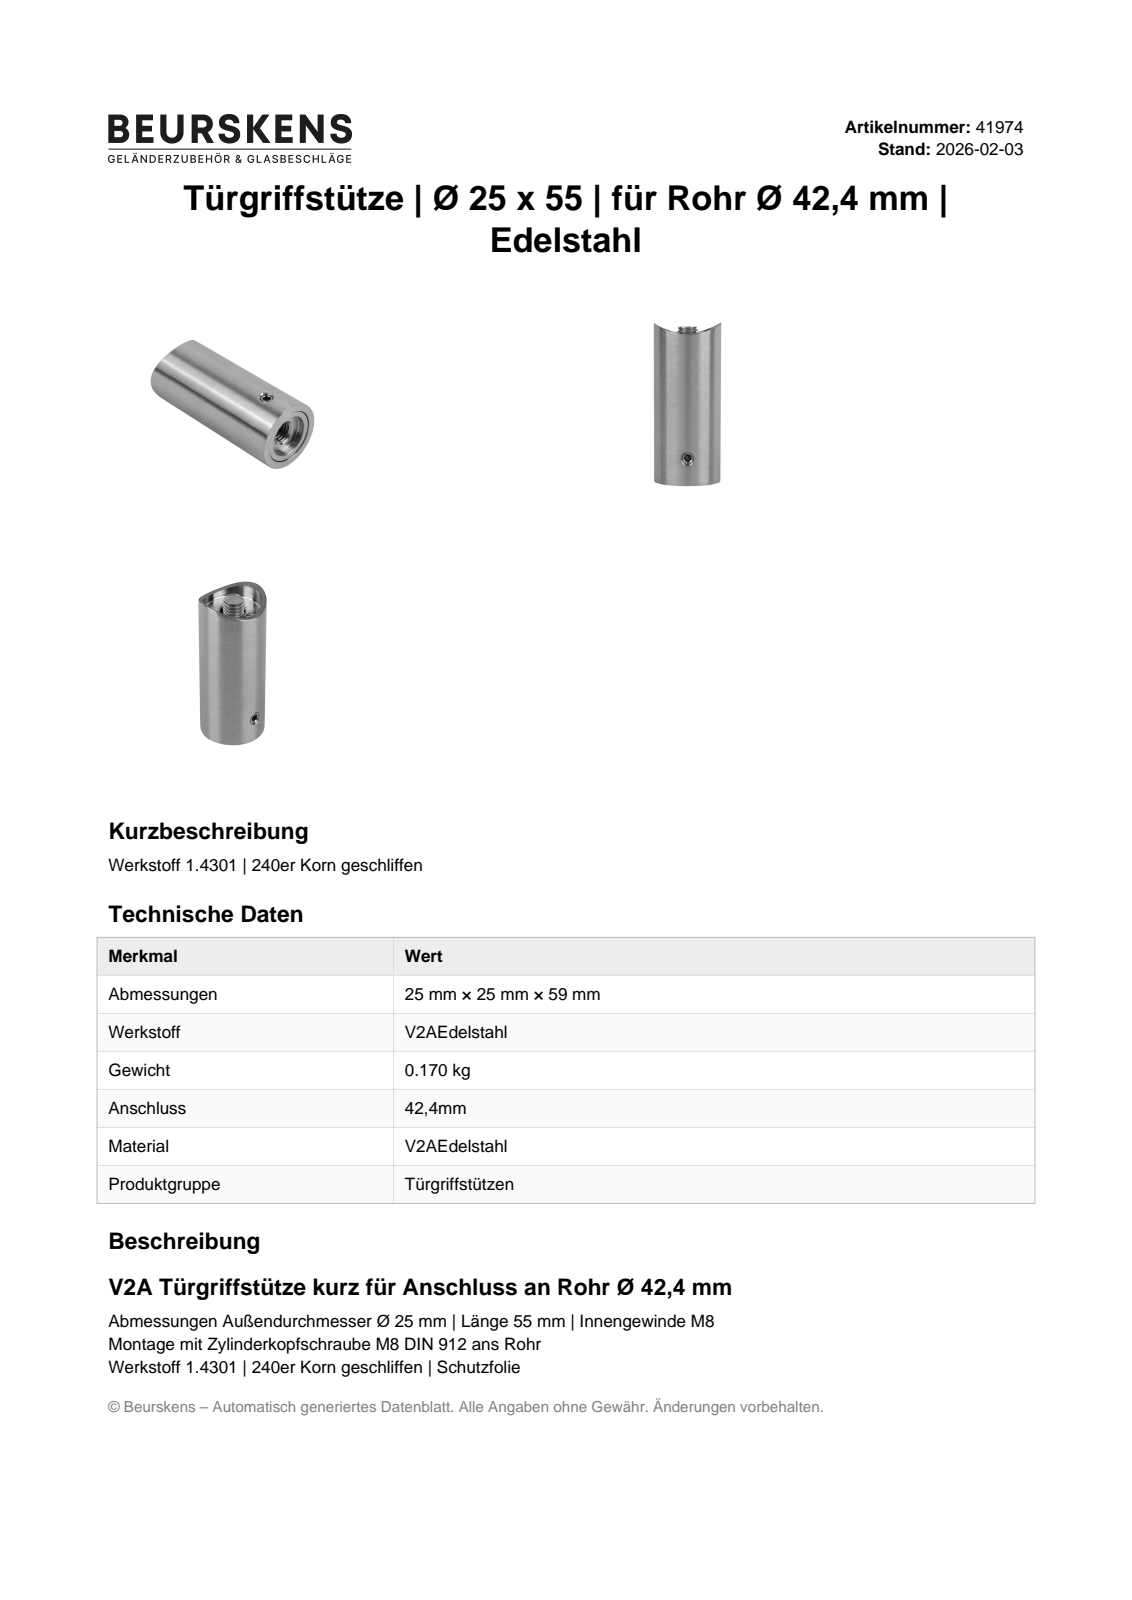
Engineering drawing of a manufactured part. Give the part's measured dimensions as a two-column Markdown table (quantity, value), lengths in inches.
| quantity | value |
| --- | --- |
| part name | 41974 |
| STEP written by | Autodesk Inventor 2022 (AUTOMOTIVE_DESIGN) |
| units | inches |
| bodies | 1 solid, 13 faces (6 planar, 7 cylindrical, 0 other) |
| overall size | 2.326 × 0.984 × 0.984 |
| volume | 1.546 in³ |
| surface area | 10.23 in² |
| round holes (diameter × count) | 0.197 × 1, 0.315 × 1, 0.791 × 1 |
| round bosses / shafts (diameter × count) | 0.984 × 1, 0.787 × 1 |
| partial cylindrical surfaces (radius × count) | 0.835 × 1 |
| main face-to-face distances | 1.378, 0.787, 0.591, 0.783, 1.374 |
